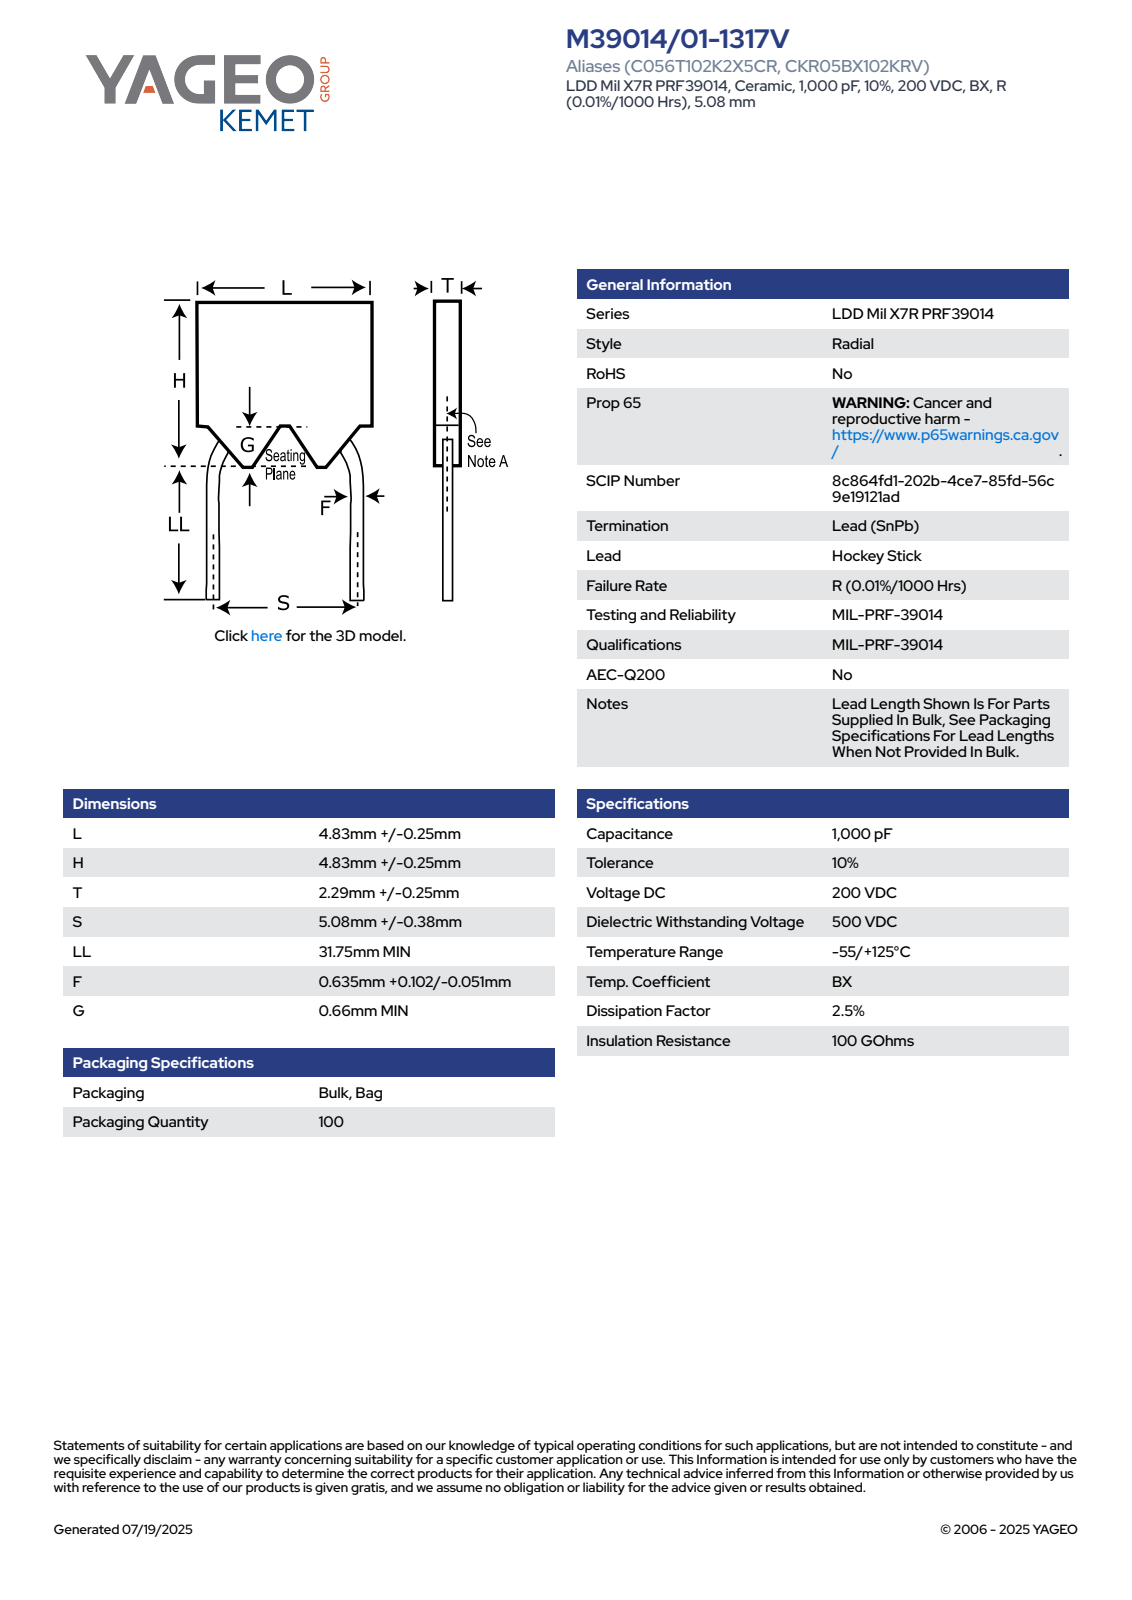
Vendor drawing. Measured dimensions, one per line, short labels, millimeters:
name: CCRM_VHS_C056_L5.08H5.74T2.54S5.08LL31.75F0.635G0.66
written by: SolidWorks 2014 (AUTOMOTIVE_DESIGN)
unit: mm
bodies: 4 solids, 85 faces (73 planar, 0 cylindrical, 12 other)
size: 37.49 × 5.66 × 2.54
volume: 88 mm³; area: 236 mm²
face distances: 2.54, 5.08, 1.48, 1.47, 0.66, 5.74, 31.75, 32.41, 37.49, 0.76
